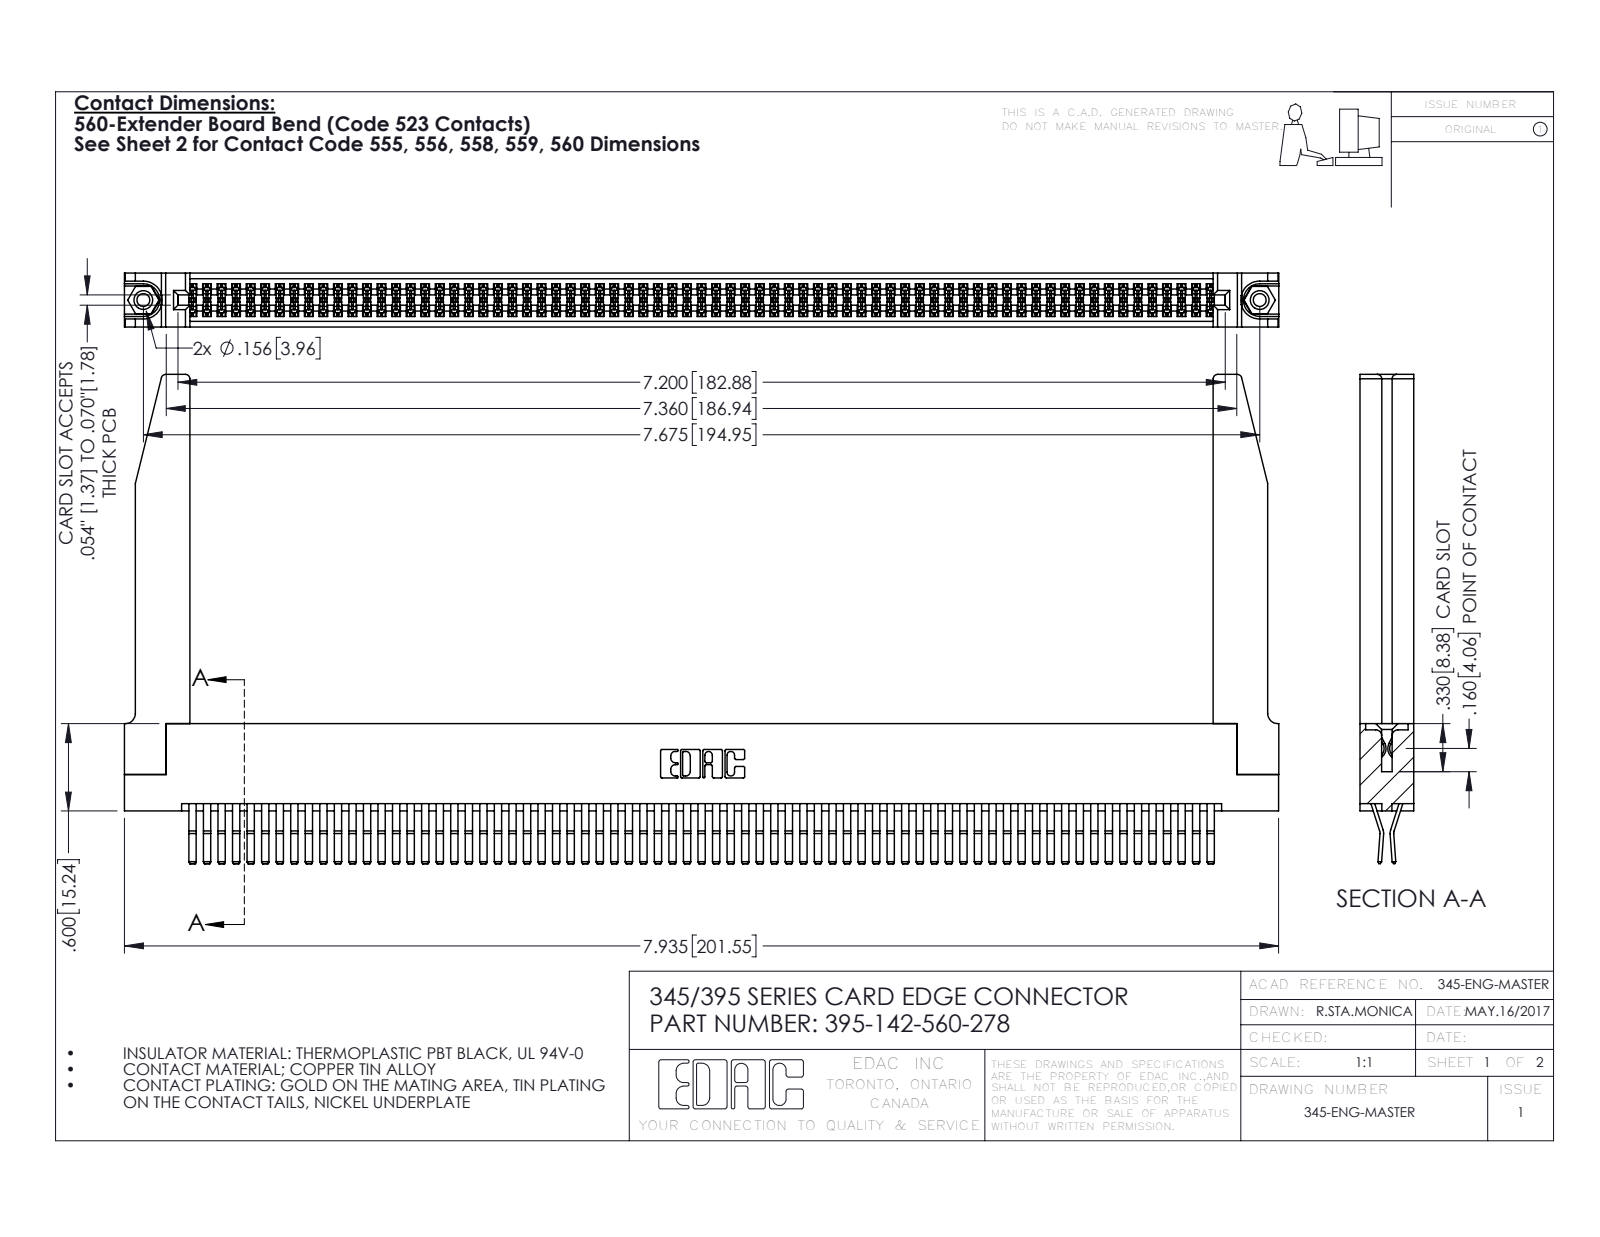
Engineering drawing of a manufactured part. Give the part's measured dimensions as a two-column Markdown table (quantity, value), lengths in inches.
| quantity | value |
| --- | --- |
| part name | 345-250-001_345-250-001-102; 345 Part_Flush Mounting Lugs - 0.156 Dia-TH; 345-292-001_560 Tail; 345-220-078_345-220-078 (+1 more) |
| STEP written by | SolidWorks 2016 (CONFIG_CONTROL_DESIGN) |
| units | inches |
| bodies | 147 solids, 7744 faces (4908 planar, 2784 cylindrical, 52 other) |
| overall size | 7.936 × 3.362 × 0.37 |
| volume | 1.742 in³ |
| surface area | 62.79 in² |
| round holes (diameter × count) | 0.089 × 2, 0.125 × 2, 0.156 × 2, 0.064 × 1 |
| round bosses / shafts (diameter × count) | 0.155 × 2 |
| partial cylindrical surfaces (radius × count) | 0.006 × 213, 0.01 × 22, 0.03 × 8, 0.007 × 6, 0.031 × 6, 0.026 × 3, 0.01 × 2, 0.014 × 2 |
| main face-to-face distances | 0.072, 0.025, 0.298, 0.37, 0.2, 0.098, 0.272, 0.225, 0.175, 0.149 |
| hole center spacings | 0.27, 7.439, 7.675 |
